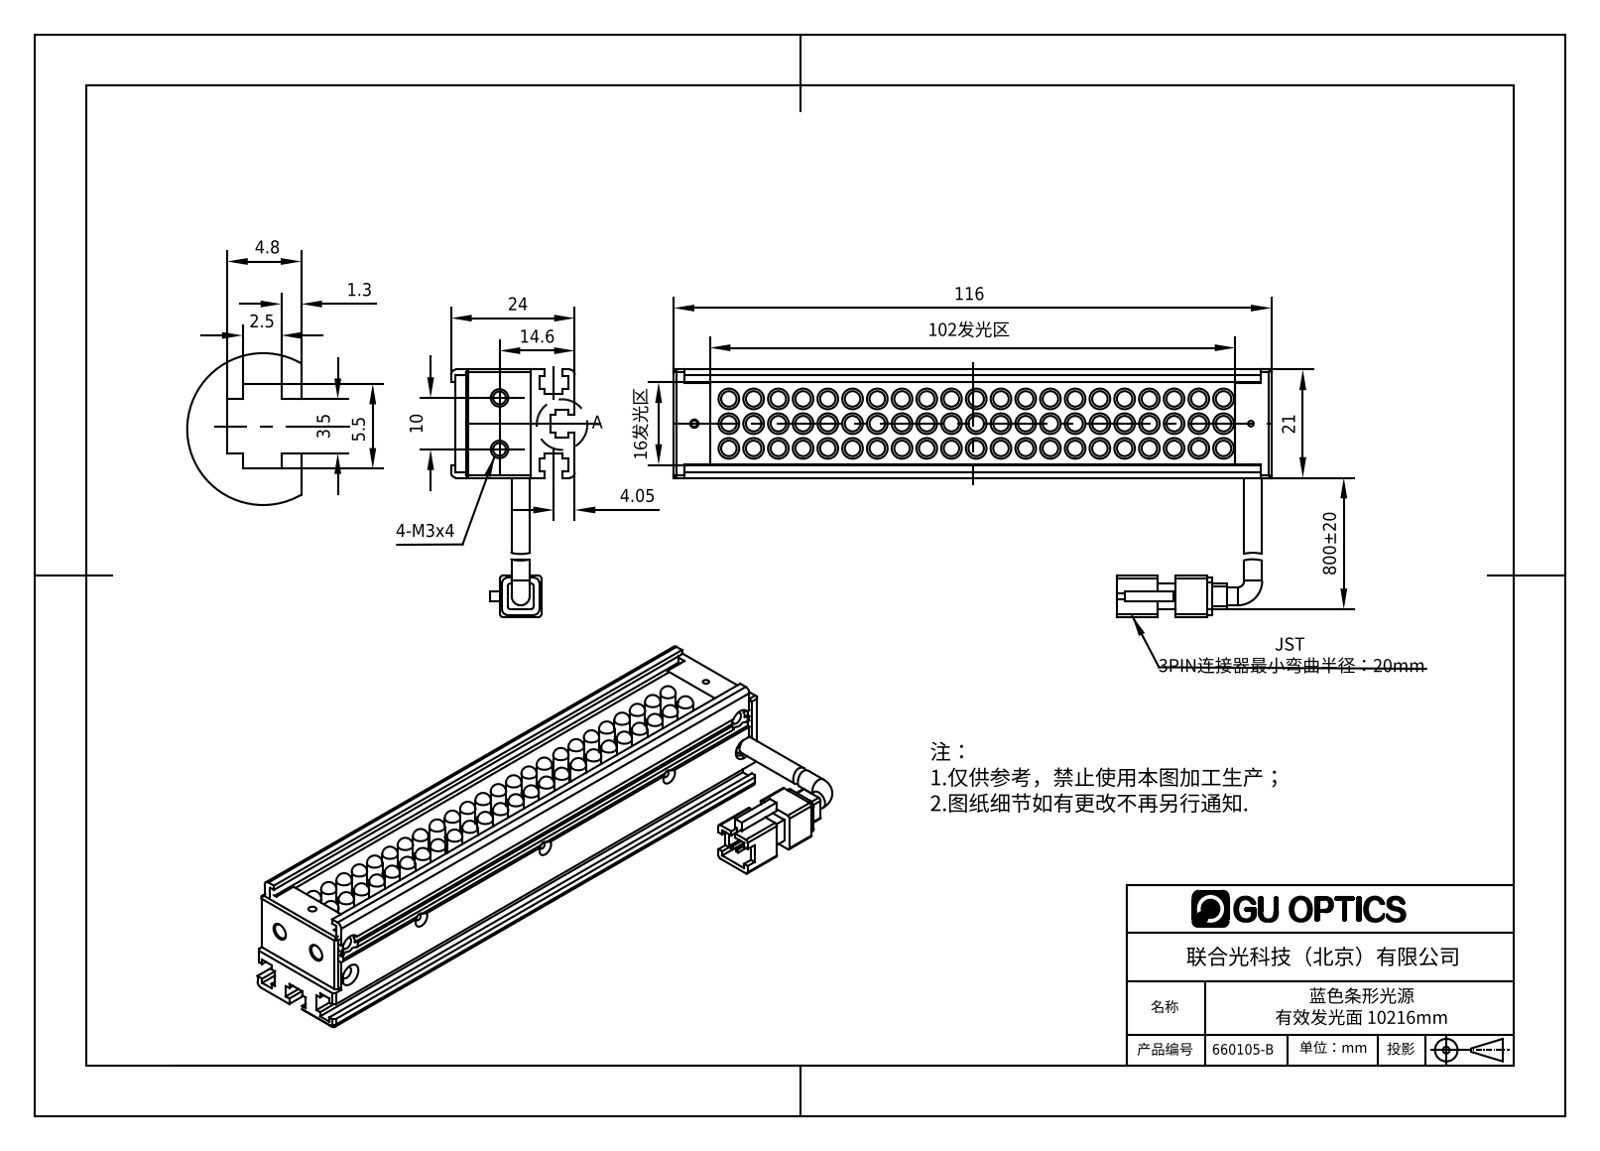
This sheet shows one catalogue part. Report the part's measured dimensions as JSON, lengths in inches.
{"part_name": "660105-B", "step_written_by": "SolidWorks 2016 (AUTOMOTIVE_DESIGN)", "units": "inches", "bodies": {"solids": 8, "faces": 1630, "planar": 1038, "cylindrical": 395, "other": 197}, "overall_size": [4.606, 1.89, 0.945], "volume_in3": 1.826, "surface_area_in2": 47.87, "round_holes": [[0.049, 5], [0.063, 5], [0.094, 4], [0.098, 2], [0.118, 2]], "round_bosses_or_shafts": [[0.157, 72], [0.118, 72], [0.138, 2]], "partial_cylinders_radius": [[0.039, 12], [0.039, 12], [0.02, 8], [0.065, 1]], "face_to_face_distances": [0.039, 0.098, 0.728, 0.138, 0.091, 0.051, 0.246, 0.827, 0.335, 0.079], "hole_center_spacings": [0.04, 0.276, 0.78, 2.111, 3.448, 4.213, 4.222, 0.269]}
